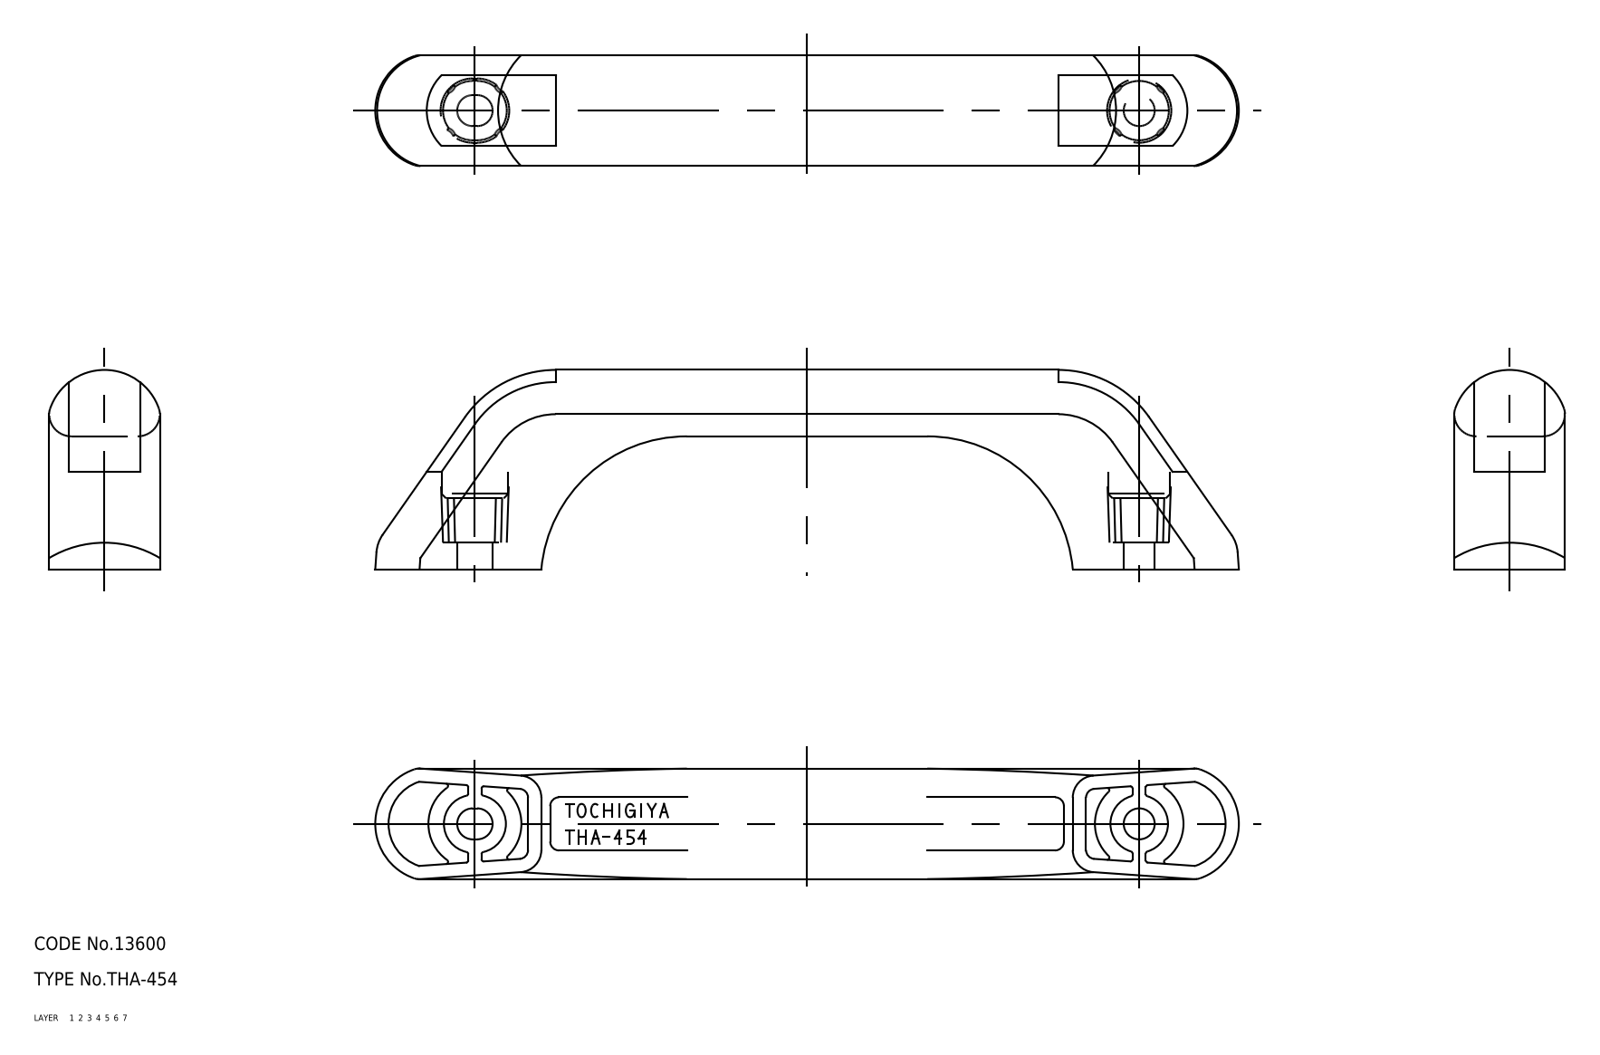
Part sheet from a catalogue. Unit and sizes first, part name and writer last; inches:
Units: inches
Overall size (bounding box): 7.677 × 1.772 × 0.984
Volume: 5.065 in³ · Surface area: 34.45 in²
Bodies: 1 solid, 190 faces (0 planar, 0 cylindrical, 190 other)
Part name (STEP PRODUCT): 67123229
STEP written by: CADfix (AUTOMOTIVE_DESIGN)
